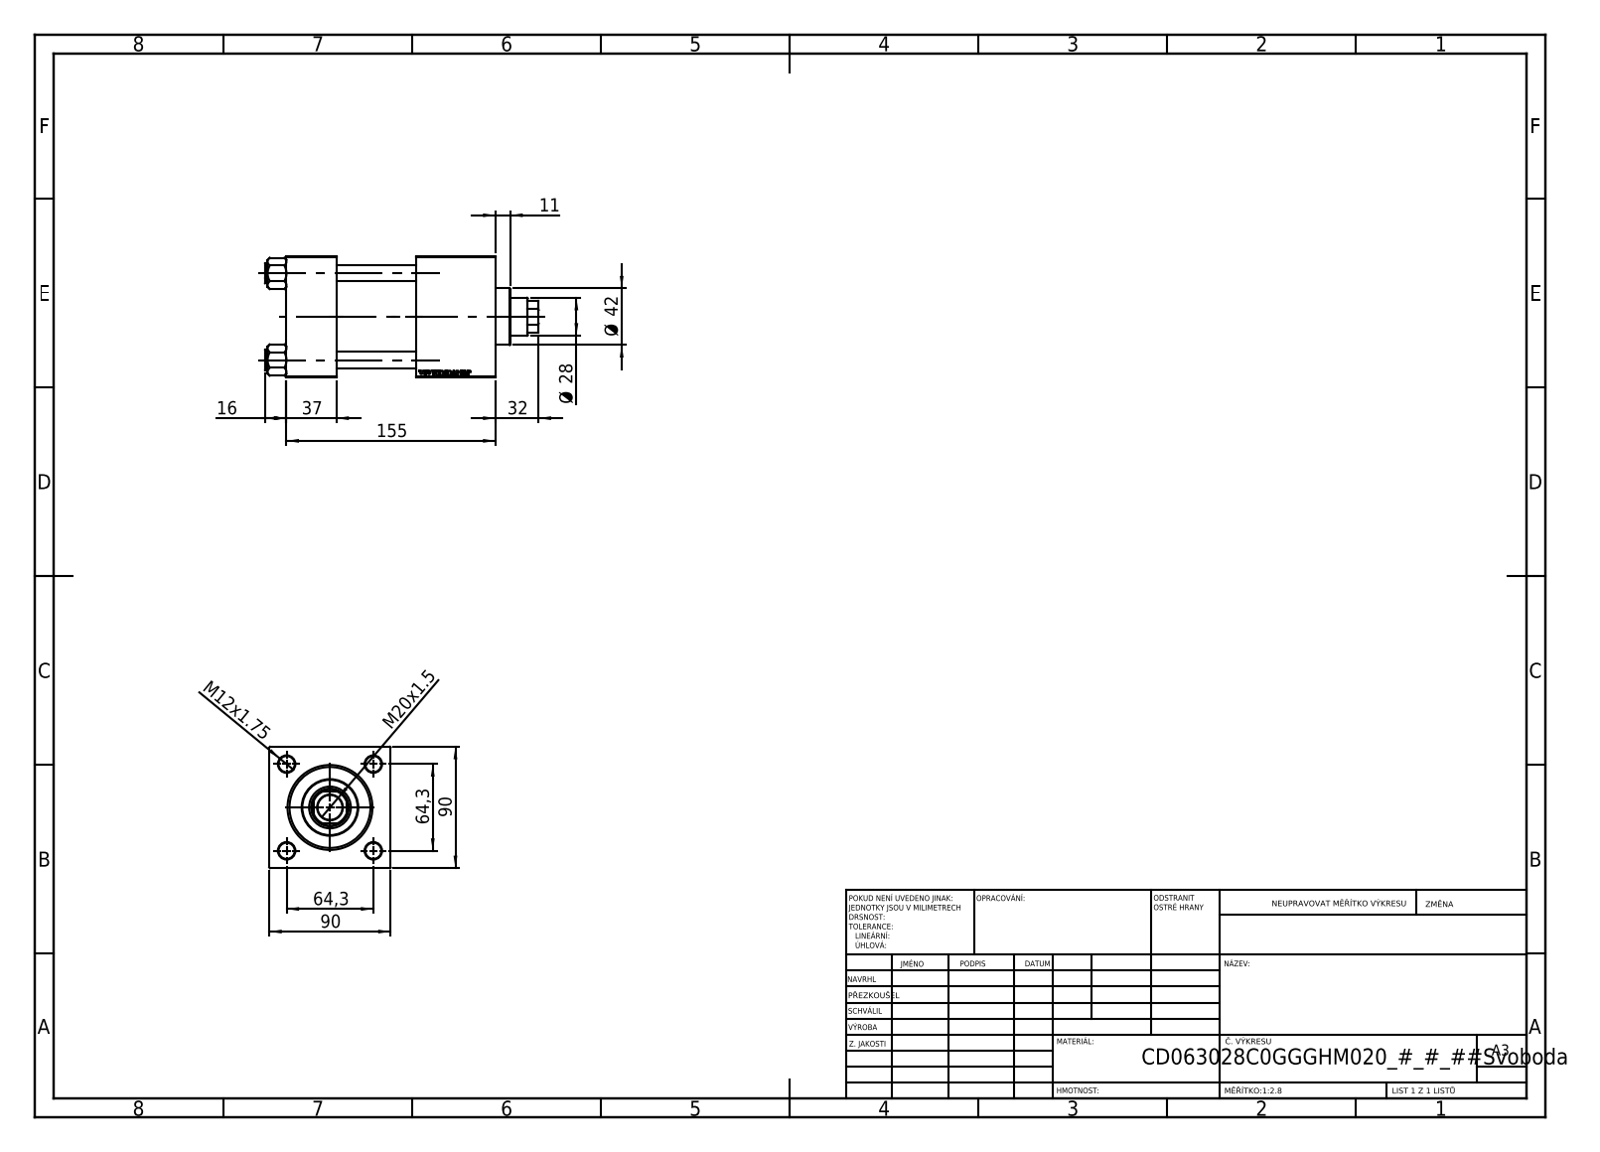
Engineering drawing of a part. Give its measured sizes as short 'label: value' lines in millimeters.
name: V215CD_C_TYCINKA; V215CD_VCP_C; V215CD_Body_C; NUT_M5_V215CD_C (+1 more)
written by: SolidWorks 2019 (CONFIG_CONTROL_DESIGN)
unit: mm
bodies: 11 solids, 1149 faces (526 planar, 87 cylindrical, 536 other)
size: 203 × 90 × 90
volume: 946 762 mm³; area: 179 134 mm²
holes: 4× ⌀12, 2× ⌀7, 2× ⌀20.96, 2× ⌀30, 1× ⌀18.5, 1× ⌀28, 1× ⌀31, 1× ⌀50, 1× ⌀60, 1× ⌀63
bosses: 4× ⌀15, 1× ⌀69, 1× ⌀42
rounds: 1× R13.5
face distances: 90, 59, 37, 155, 118, 96, 126.3, 89.3, 30.3, 28.7
hole spacings: 45.47, 64.3, 90.93, 97.5
